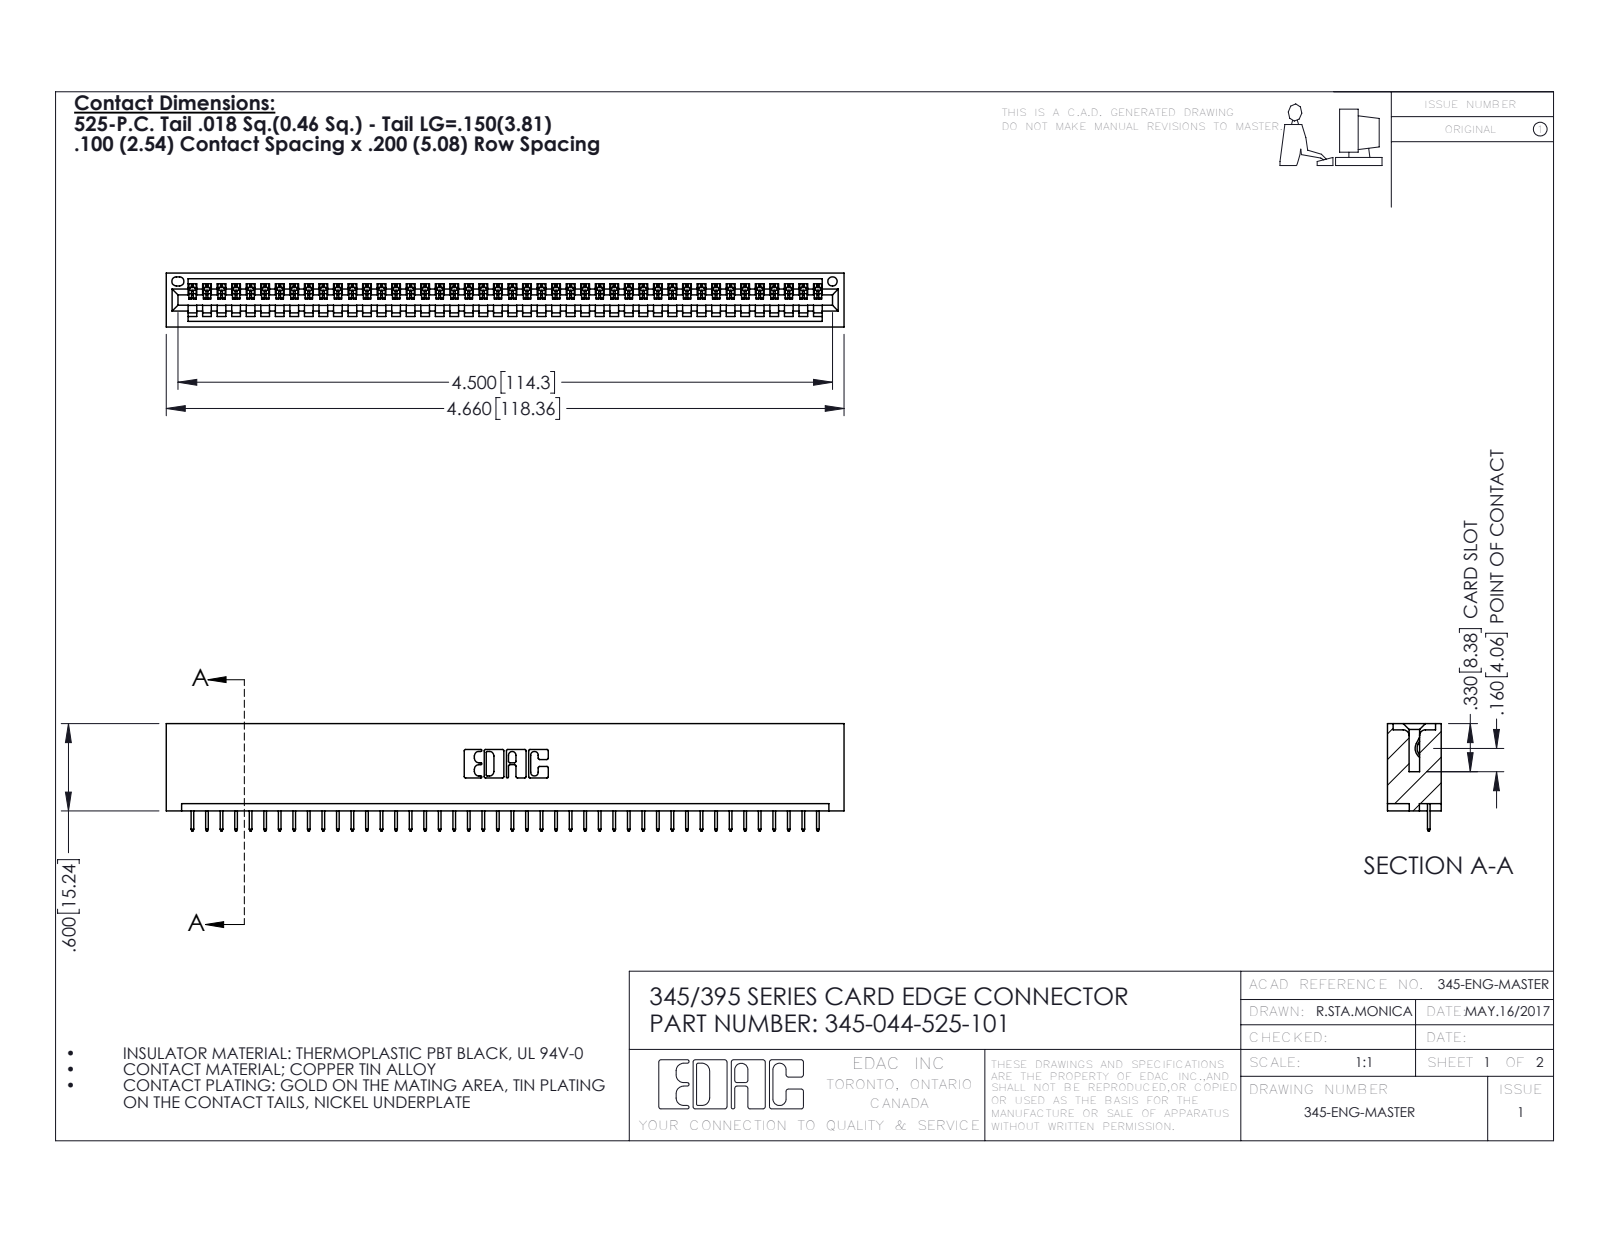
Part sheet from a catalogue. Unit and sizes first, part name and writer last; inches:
Units: inches
Overall size (bounding box): 4.66 × 0.737 × 0.37
Round holes (diameter × count): ⌀0.064 ×1
Partial cylindrical surfaces — rounded edges, fillets, slot ends (radius × count): R0.006 ×88, R0.01 ×22, R0.007 ×6, R0.031 ×6, R0.026 ×3, R0.031 ×2, R0.04 ×2, R0.014 ×1
Main face-to-face distances: 0.298, 0.072, 0.37, 0.2, 0.098, 0.272, 0.025, 0.225, 0.072, 0.149
Volume: 0.712 in³ · Surface area: 23.43 in²
Bodies: 45 solids, 2846 faces (2100 planar, 746 cylindrical, 0 other)
Part name (STEP PRODUCT): 345-044-525-101; 345-292-001_345-293-125; 345 Part_No Mounting Lugs
STEP written by: SolidWorks 2020 (CONFIG_CONTROL_DESIGN)
